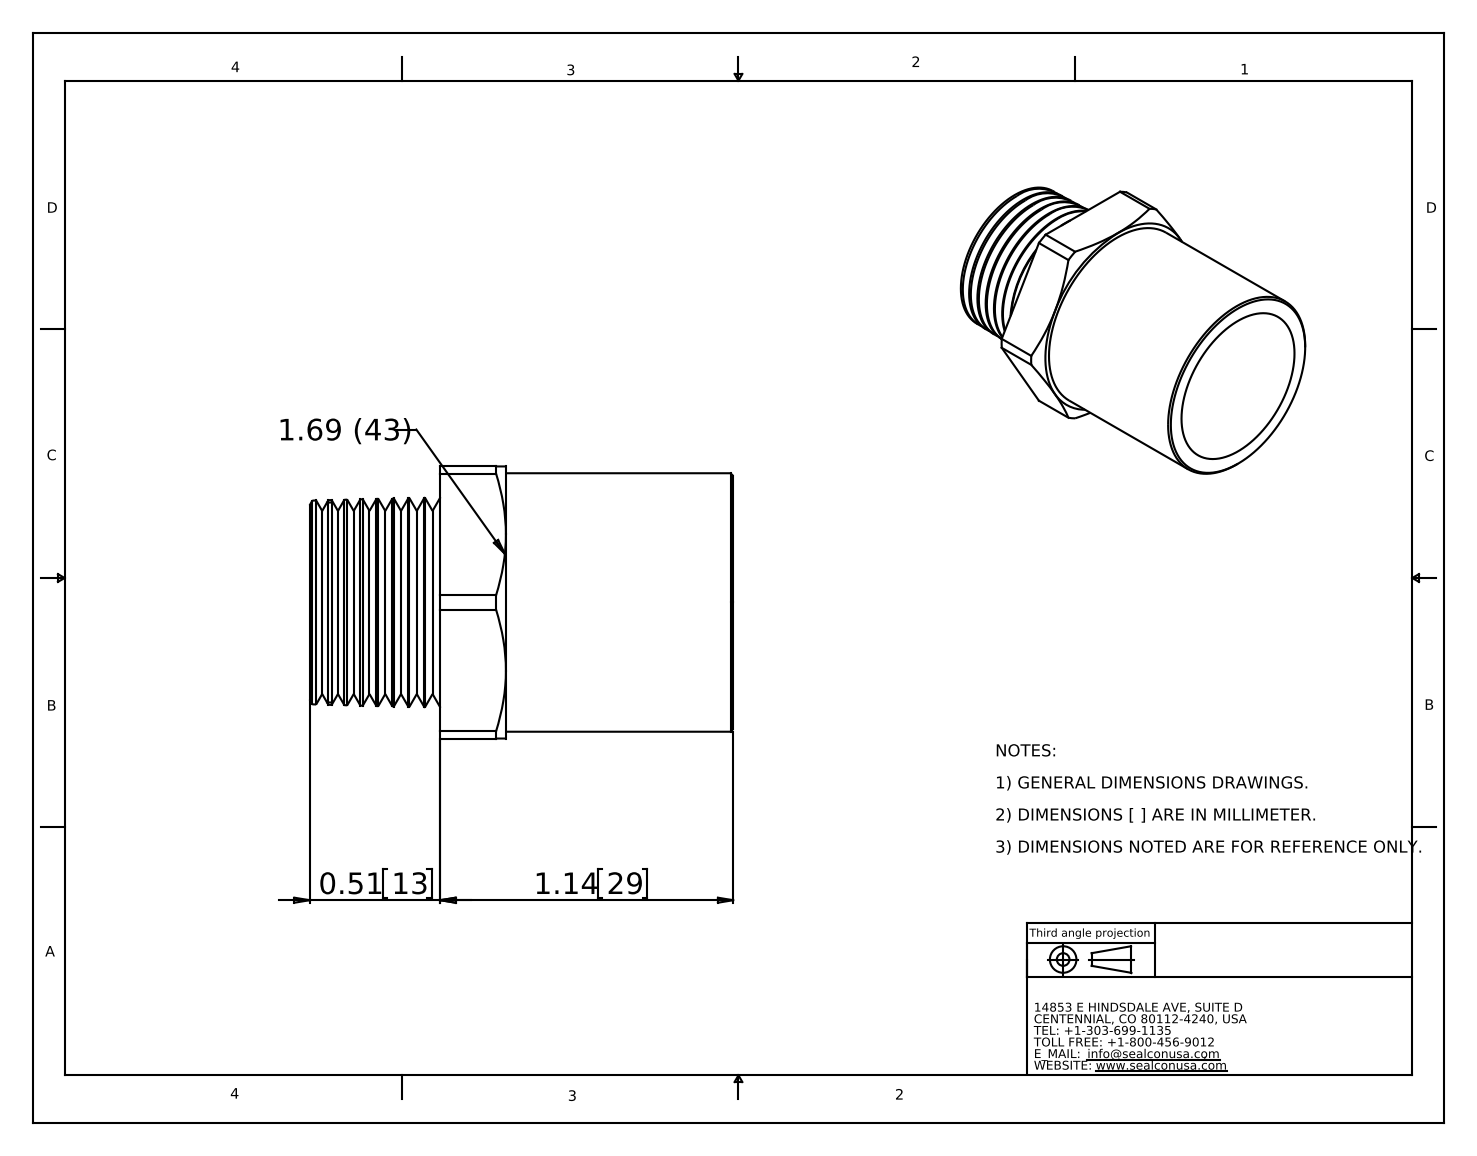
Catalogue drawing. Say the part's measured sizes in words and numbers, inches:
The part is named "SM16NA-BK". Its 3-D file was written by "SolidWorks 2007 (AUTOMOTIVE_DESIGN)". It is 1 solid with 83 faces: 11 planar, 11 cylindrical and 61 other. Overall it measures 1.65 by 1.193 by 1.06 inches. Its volume is 0.554 cubic inches and its surface area 10.93 square inches. Round holes: 1 of diameter 0.83. Round bosses or shafts: 1 of diameter 1.007. Partial cylindrical surfaces (rounded edges, fillets, slot ends): 1 of radius 0.596. The main face-to-face distances are 0.255, 1.06, 0.885, 1.14, 1.65, 0.765, 0.51.
